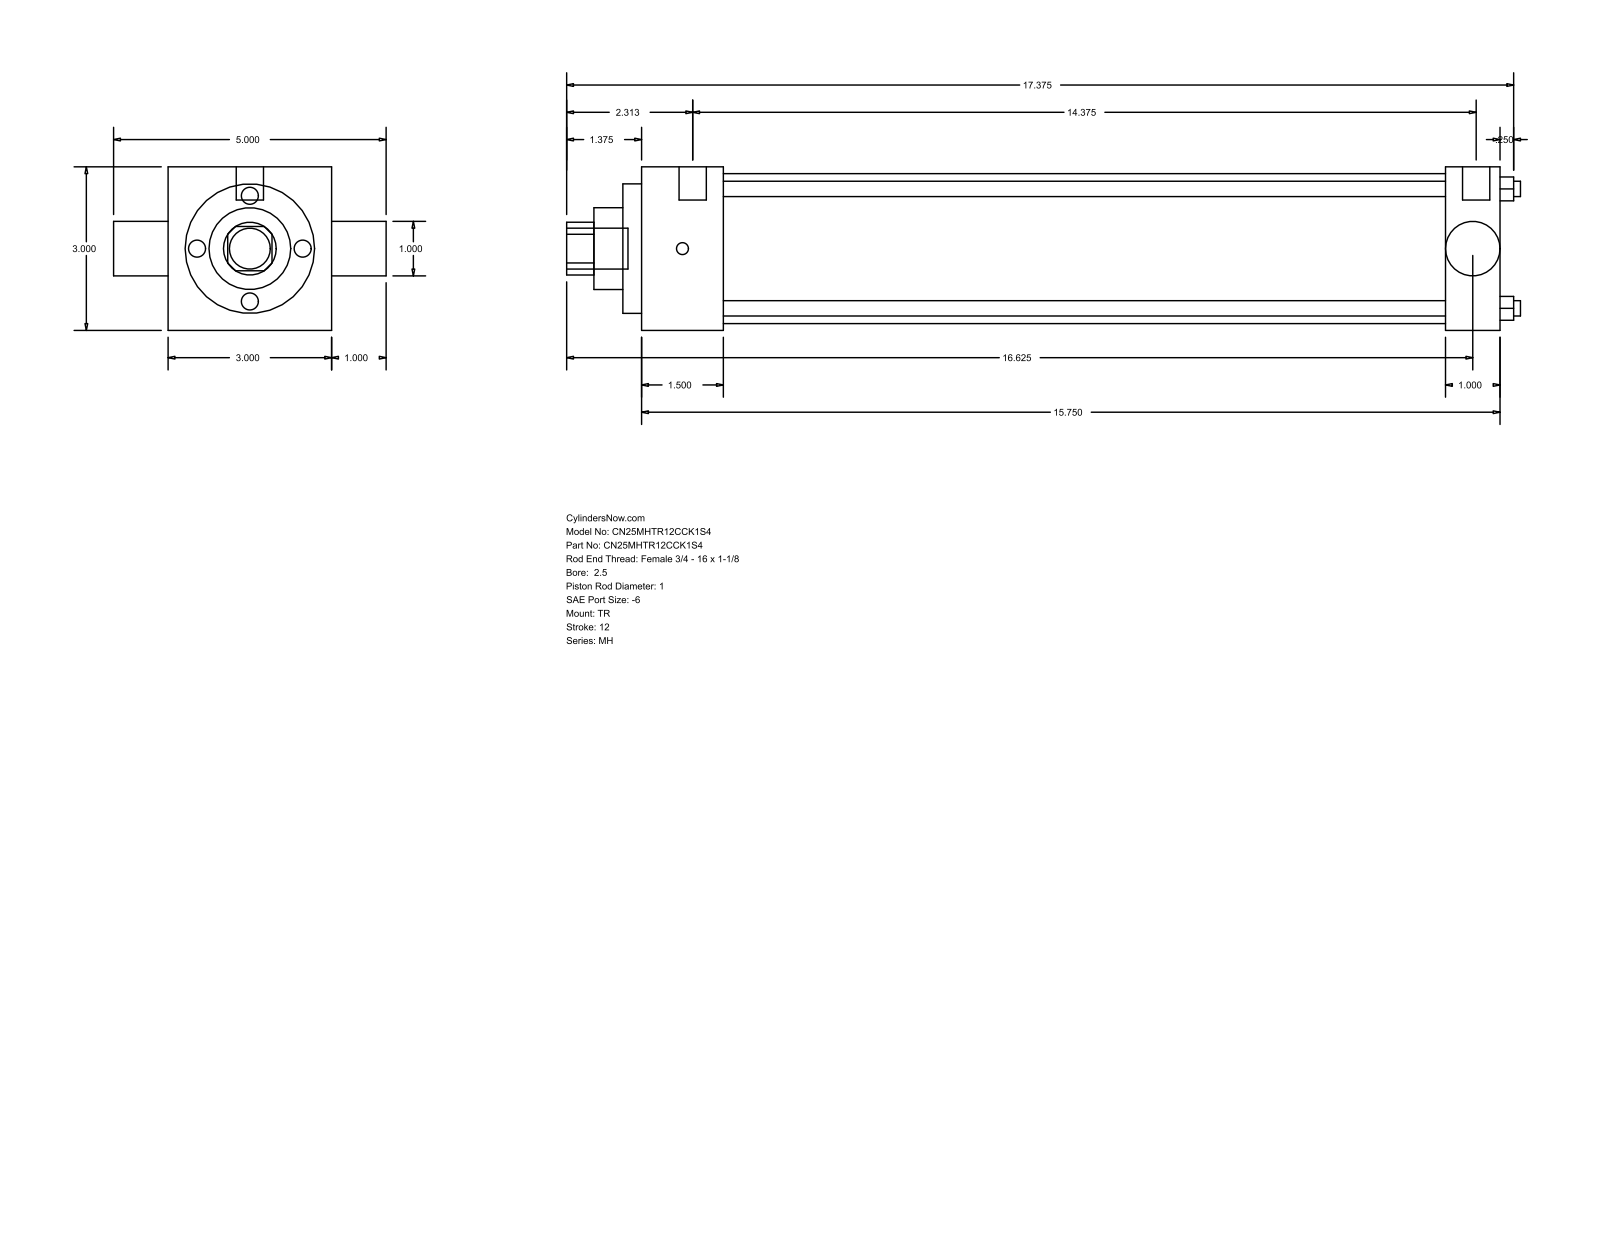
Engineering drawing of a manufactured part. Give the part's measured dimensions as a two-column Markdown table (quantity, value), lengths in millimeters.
| quantity | value |
| --- | --- |
| part name | MH_TR__0250_1 |
| STEP written by | GSSL Pune (CONFIG_CONTROL_DESIGN) |
| units | millimeters |
| bodies | 0 solids, 86 faces (61 planar, 25 cylindrical, 0 other) |
| overall size | 444.5 × 127 × 76.2 |
| round holes (diameter × count) | 7.14 × 4, 25.35 × 1, 25.4 × 1, 38.1 × 1, 60.33 × 1, 69.85 × 1 |
| round bosses / shafts (diameter × count) | 5.56 × 3, 12.7 × 2, 19.05 × 1 |
| partial cylindrical surfaces (radius × count) | 12.29 × 1 |
| main face-to-face distances | 76.2, 400.06, 38.11, 361.95, 374.65, 336.54, 25.41, 8.73, 46.84, 383.38 |
| hole center spacings | 39.33, 55.62, 78.66 |
